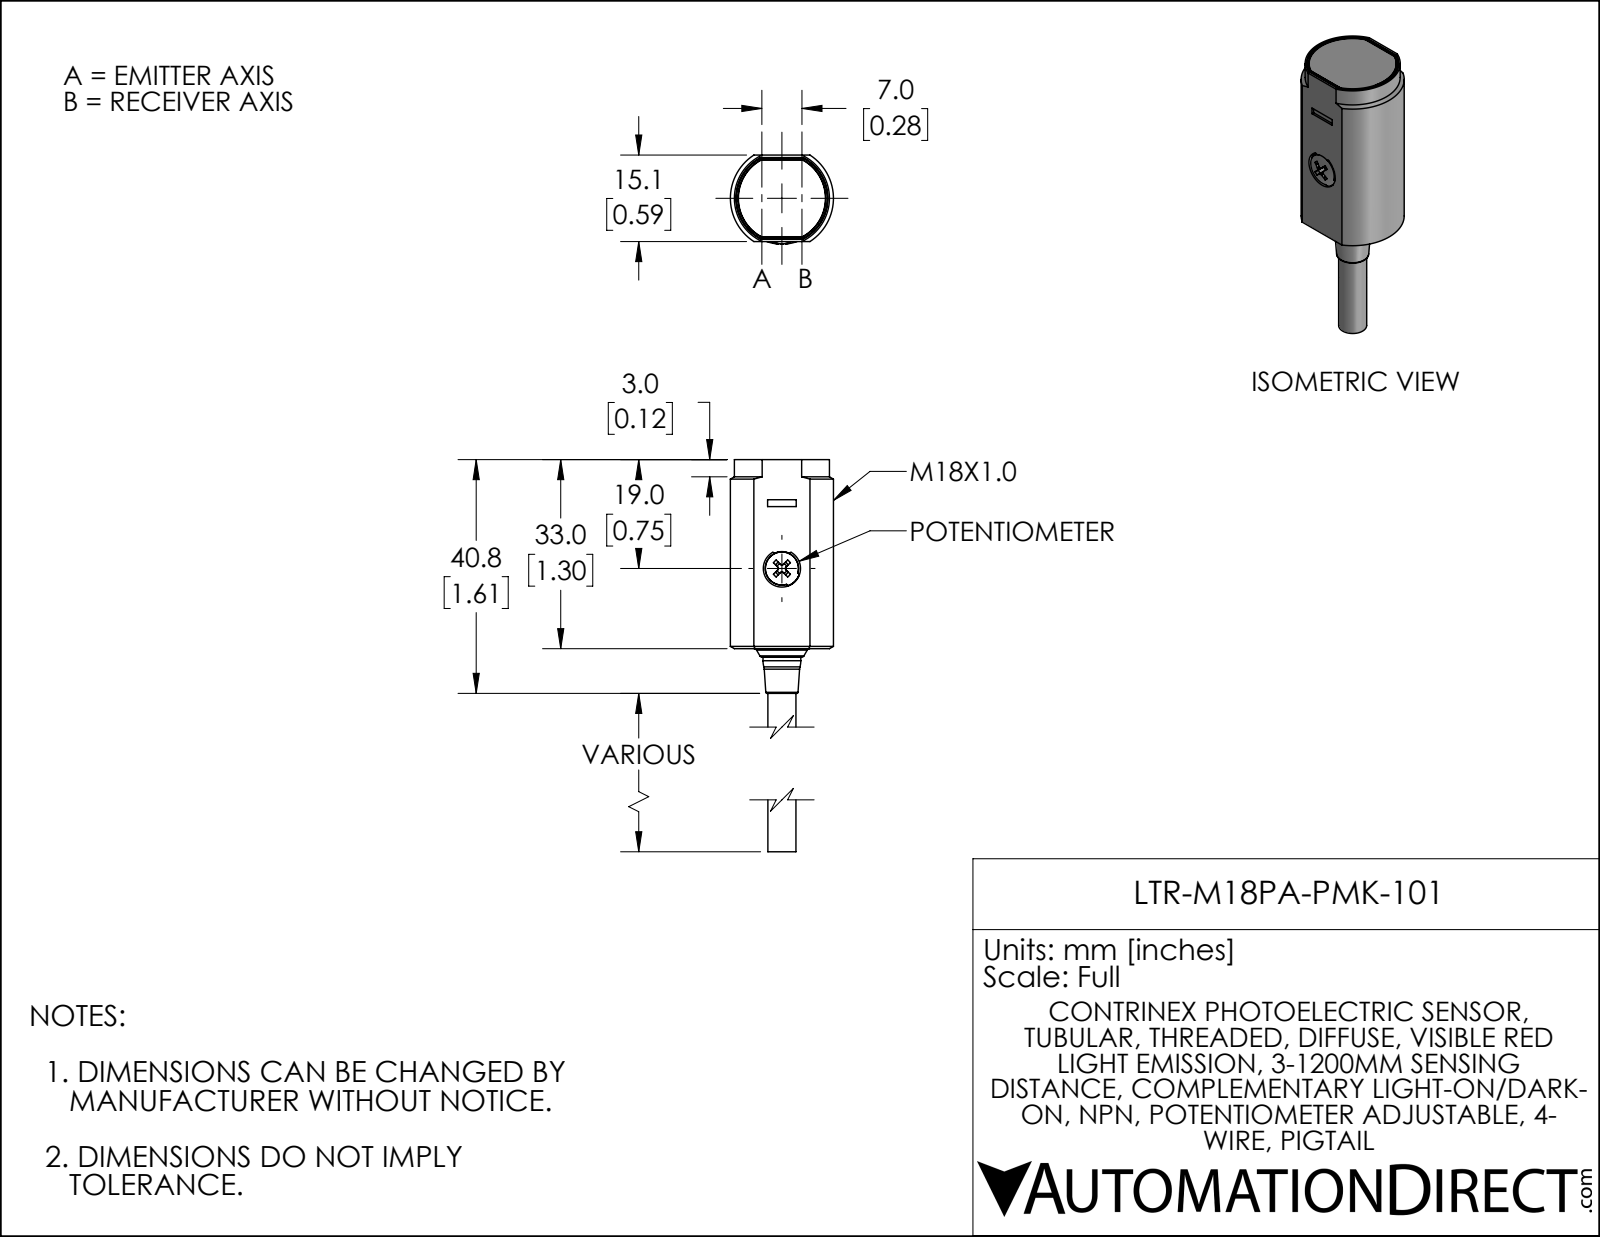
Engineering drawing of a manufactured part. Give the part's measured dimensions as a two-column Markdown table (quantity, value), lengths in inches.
| quantity | value |
| --- | --- |
| part name | LTR-M18PA-PMK-101 |
| STEP written by | SolidWorks 2021 (AUTOMOTIVE_DESIGN) |
| units | inches |
| bodies | 1 solid, 116 faces (58 planar, 40 cylindrical, 18 other) |
| overall size | 2.205 × 0.709 × 0.611 |
| volume | 0.5 in³ |
| surface area | 4.262 in² |
| round holes (diameter × count) | 0.256 × 1 |
| round bosses / shafts (diameter × count) | 0.26 × 1, 0.193 × 1 |
| partial cylindrical surfaces (radius × count) | 0.014 × 8, 0.028 × 8, 0.006 × 4, 0.024 × 4, 0.116 × 1, 0.299 × 1, 0.302 × 1, 0.313 × 1 |
| main face-to-face distances | 0.594, 1.297, 0.016, 1.299, 2.205, 2.203, 0.906, 0.579, 0.563, 0.014 |
